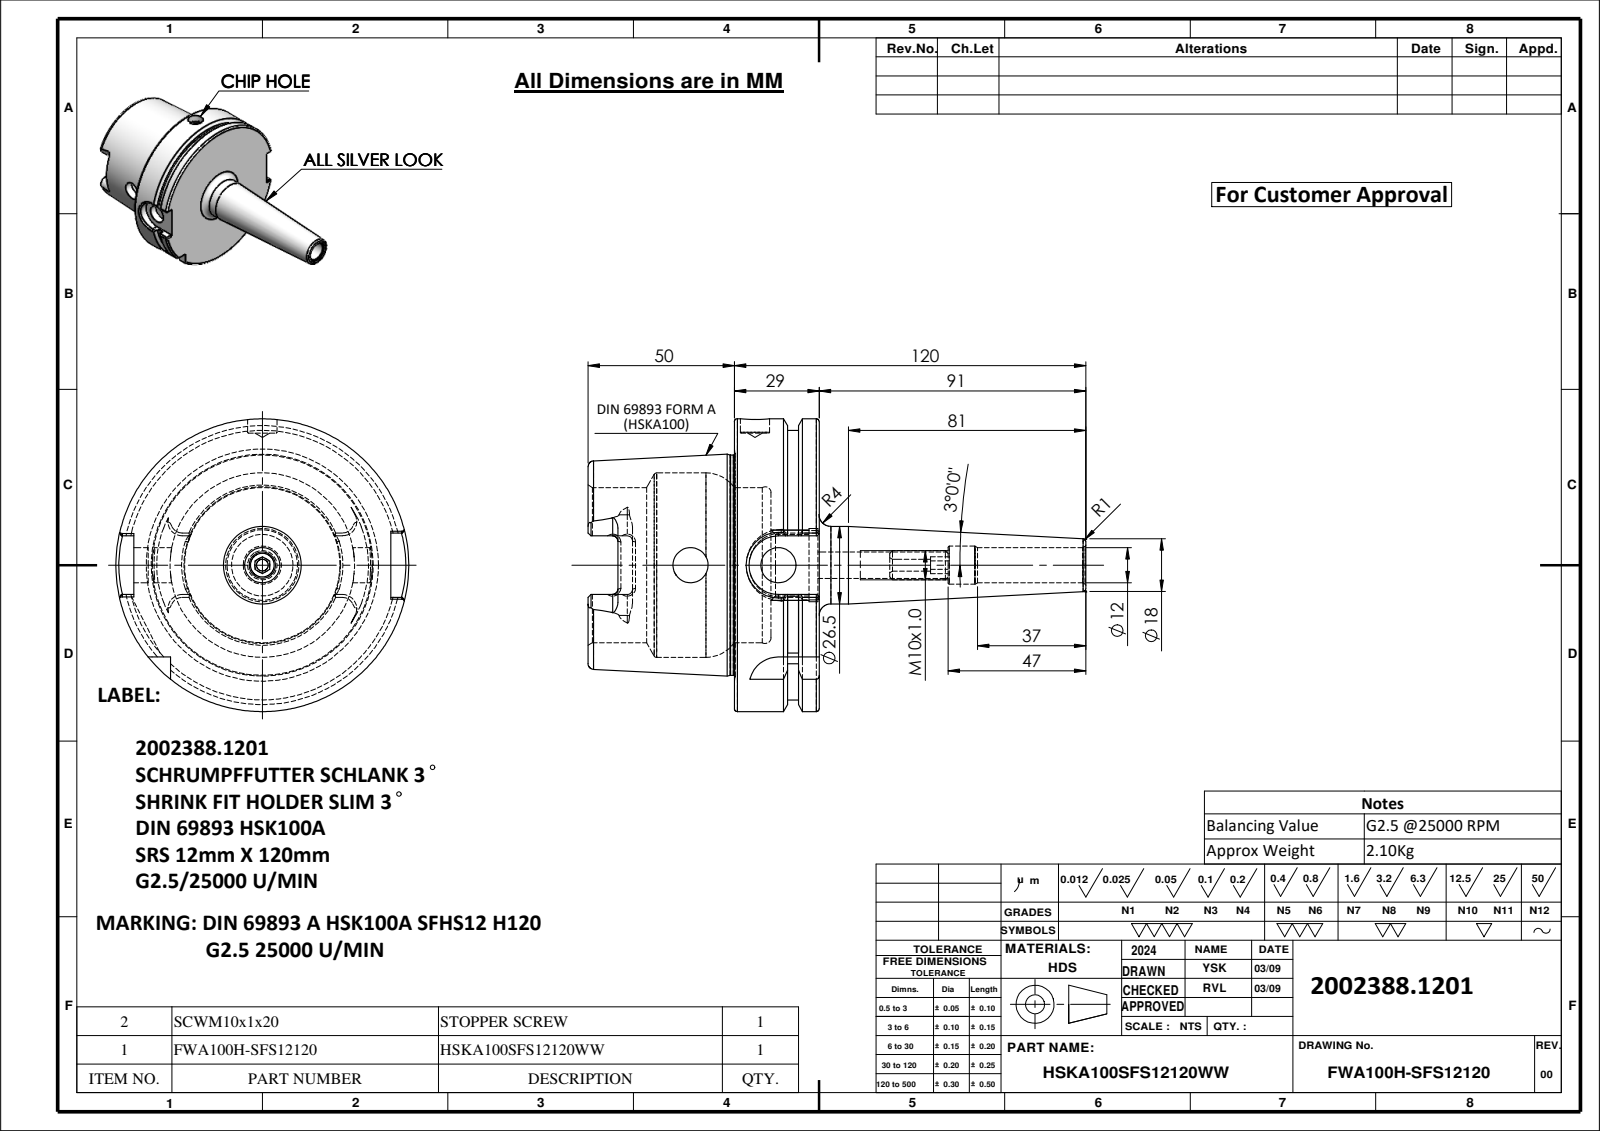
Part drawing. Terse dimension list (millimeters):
name: HSKA100SFS12120WW; SCWM10X1; FWA100H-SFS12120
written by: SolidWorks 2024 (CONFIG_CONTROL_DESIGN)
unit: mm
bodies: 2 solids, 201 faces (61 planar, 56 cylindrical, 84 other)
size: 170 × 100 × 100
volume: 284 243 mm³; area: 59 873 mm²
holes: 3× ⌀12, 1× ⌀4, 1× ⌀9, 1× ⌀10, 1× ⌀13, 1× ⌀21, 1× ⌀25, 1× ⌀53, 1× ⌀63
bosses: 1× ⌀100, 1× ⌀92, 1× ⌀75.16, 1× ⌀26.5, 1× ⌀10
rounds: 6× R1.8, 4× R4.88, 2× R10, 1× R11
face distances: 28.95, 12.5, 16.45, 50, 62.5, 78.95, 78.5, 28.5, 16, 0.45
hole spacings: 30
